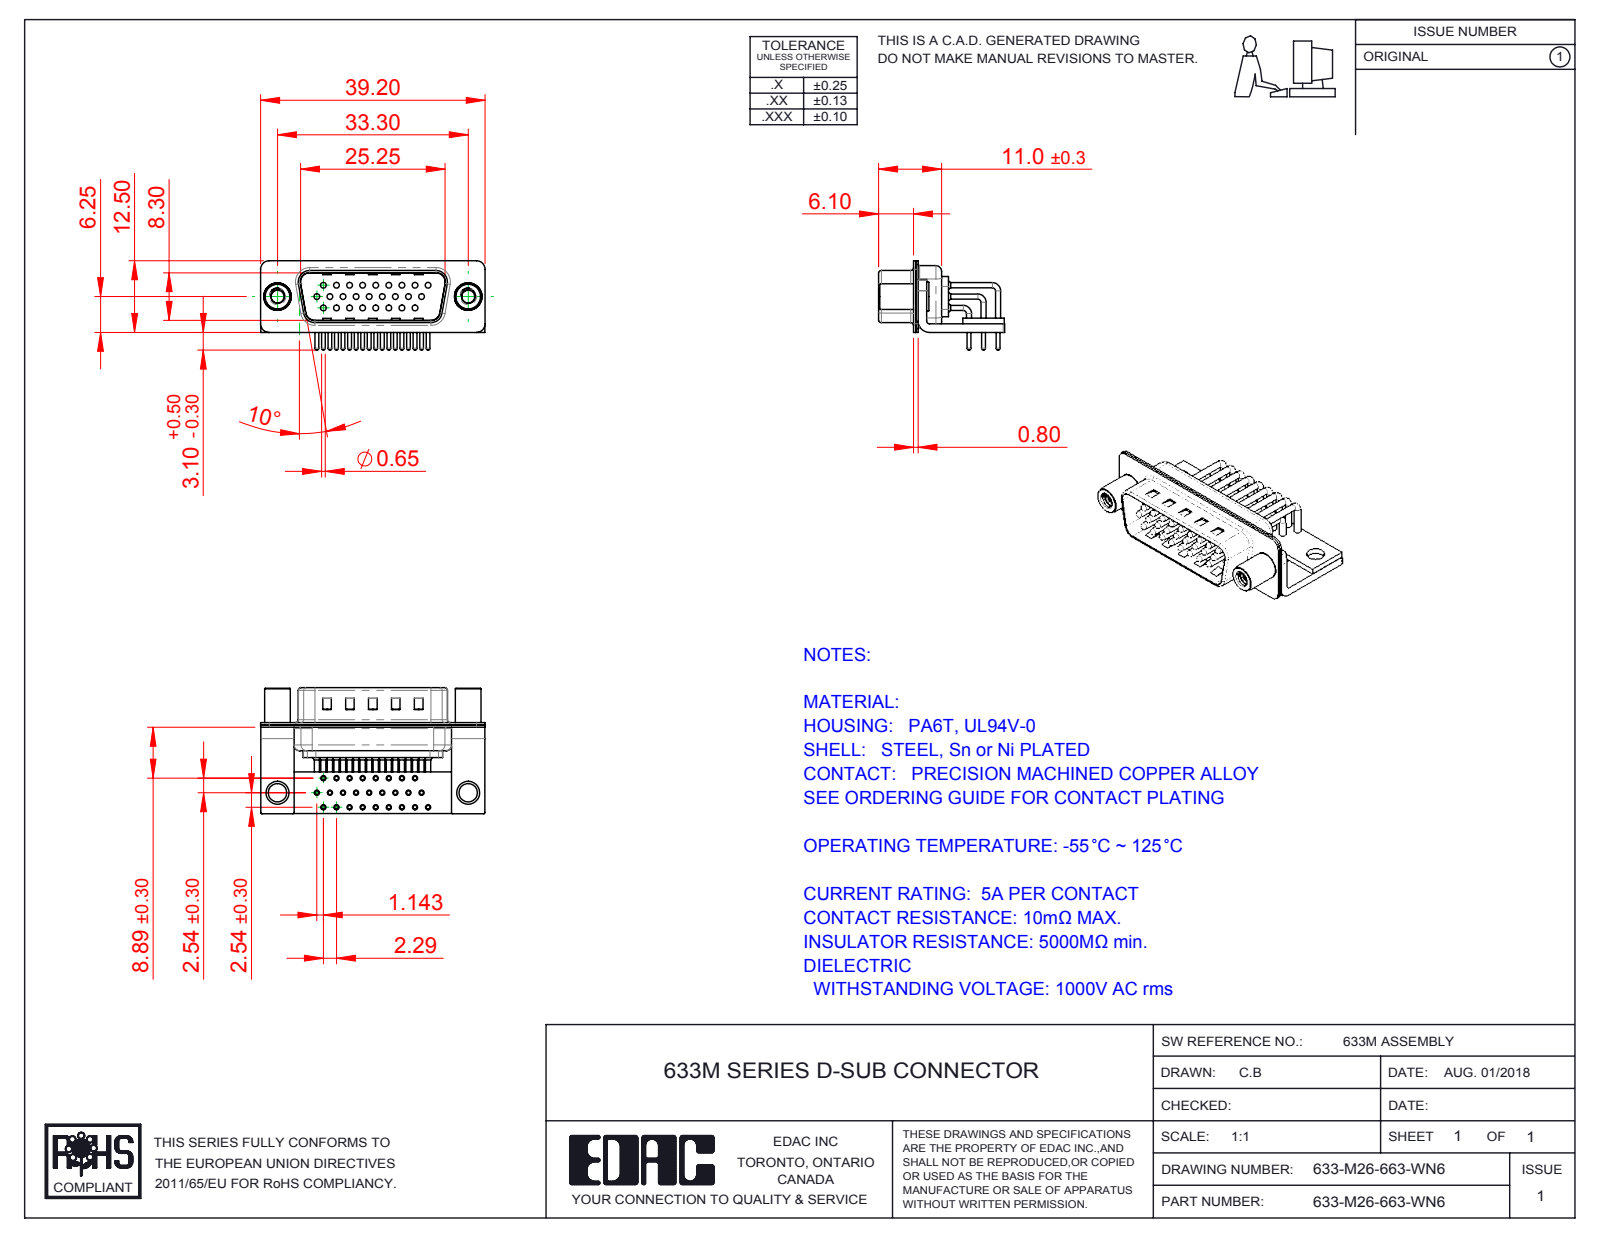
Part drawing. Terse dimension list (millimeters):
name: 633M Stabilizer Board_26 Contacts; 633M Contact Row 1; 633M Stabilizer Bracket; 633M Contact Row 2 (+6 more)
written by: SolidWorks 2016 (CONFIG_CONTROL_DESIGN)
unit: mm
bodies: 34 solids, 3352 faces (1831 planar, 1185 cylindrical, 336 other)
size: 39.2 × 22 × 15.6
volume: 2 748 mm³; area: 8 315 mm²
holes: 26× ⌀0.9, 26× ⌀1, 26× ⌀1.7, 26× ⌀2, 2× ⌀2.26, 2× ⌀3.2, 2× ⌀4, 2× ⌀4.8
bosses: 26× ⌀1.5, 26× ⌀0.9, 26× ⌀0.65, 2× ⌀5, 2× ⌀4.9, 2× ⌀4.5
rounds: 26× R1.01, 16× R0.25, 16× R1.5, 13× R2, 9× R0.5, 8× R1.6, 4× R0.6, 4× R0.65
face distances: 0.4, 1.5, 0.85, 0.8, 1.25, 1, 1.9, 10.4, 9.55, 2.5
hole spacings: 4.57, 2.29, 2.28, 3.96, 6.86, 4.27, 6.05, 2.78
